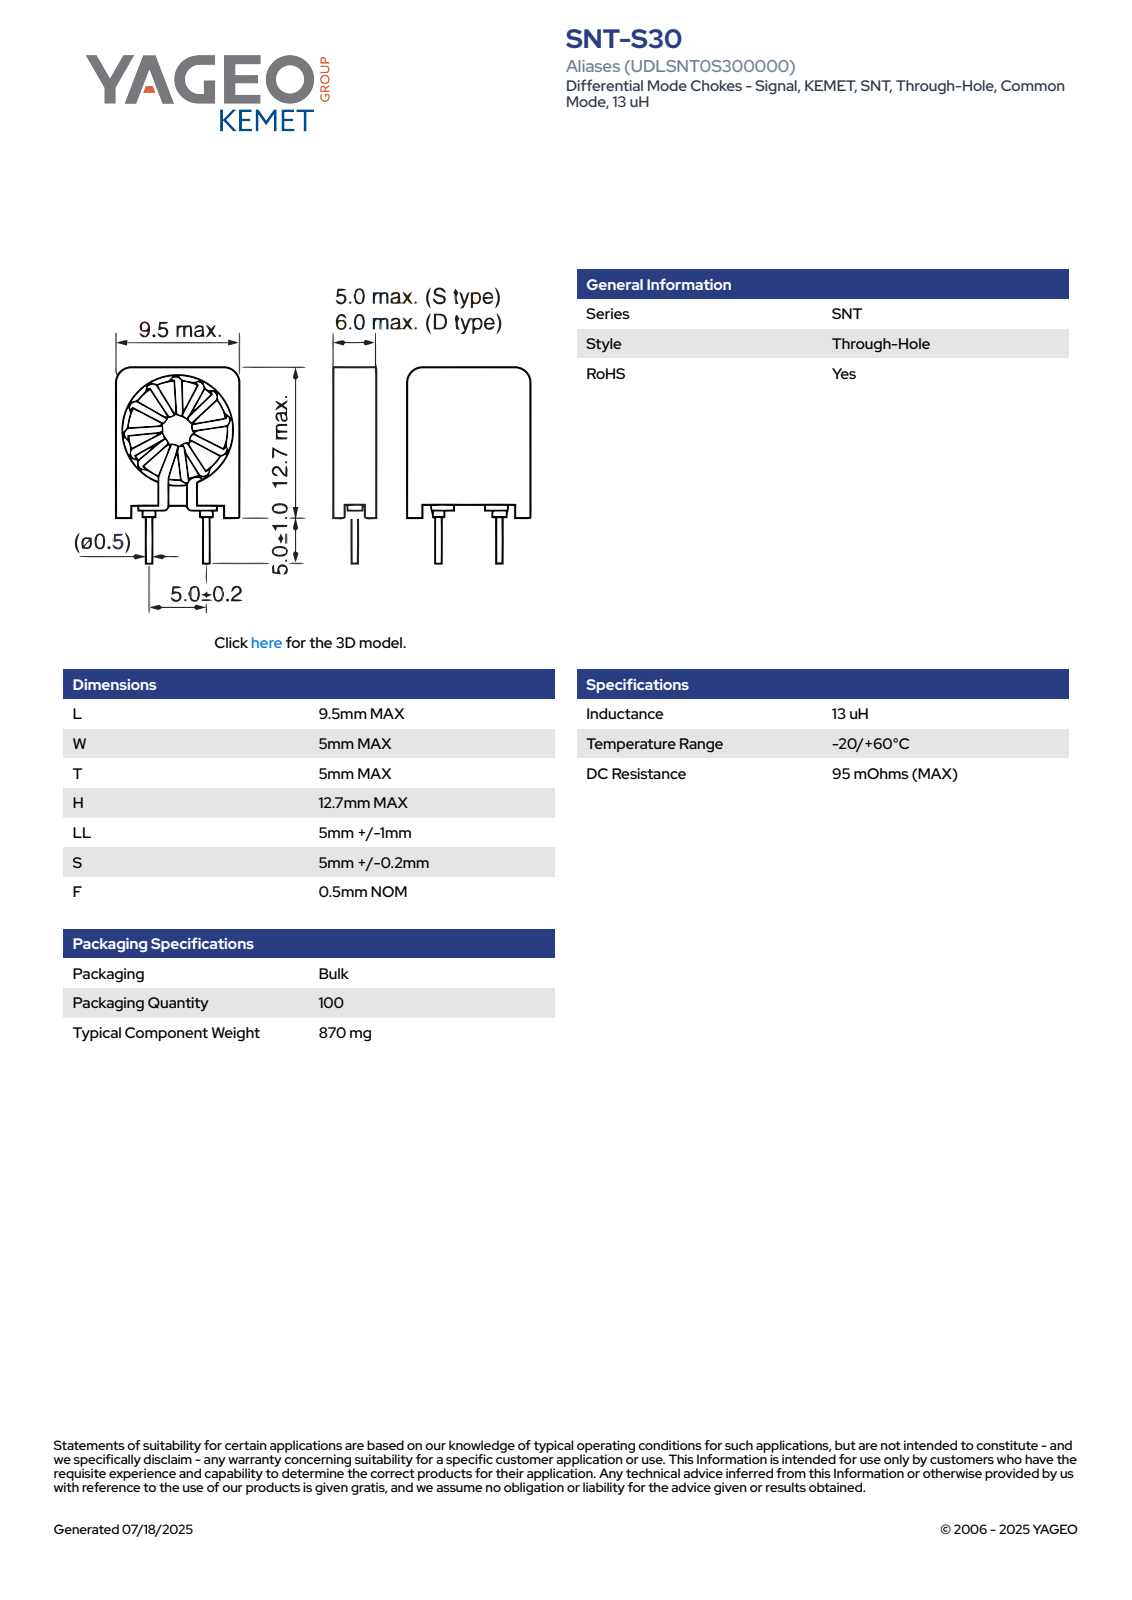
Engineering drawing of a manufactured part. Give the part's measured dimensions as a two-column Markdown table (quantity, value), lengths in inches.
| quantity | value |
| --- | --- |
| part name | IFC_NTSNT_L9.5W5T5 |
| STEP written by | SolidWorks 2014 (AUTOMOTIVE_DESIGN) |
| units | inches |
| bodies | 1 solid, 498 faces (214 planar, 199 cylindrical, 85 other) |
| overall size | 0.736 × 0.374 × 0.197 |
| volume | 0.031 in³ |
| surface area | 1.04 in² |
| round holes (diameter × count) | 0.093 × 1, 0.335 × 1 |
| round bosses / shafts (diameter × count) | 0.02 × 2, 0.291 × 1, 0.069 × 1 |
| partial cylindrical surfaces (radius × count) | 0.02 × 32, 0.024 × 32, 0.01 × 20, 0.02 × 2 |
| main face-to-face distances | 0.374, 0.098, 0.197, 0.472, 0.189, 0.091, 0.042, 0.159, 0.117, 0.257 |
